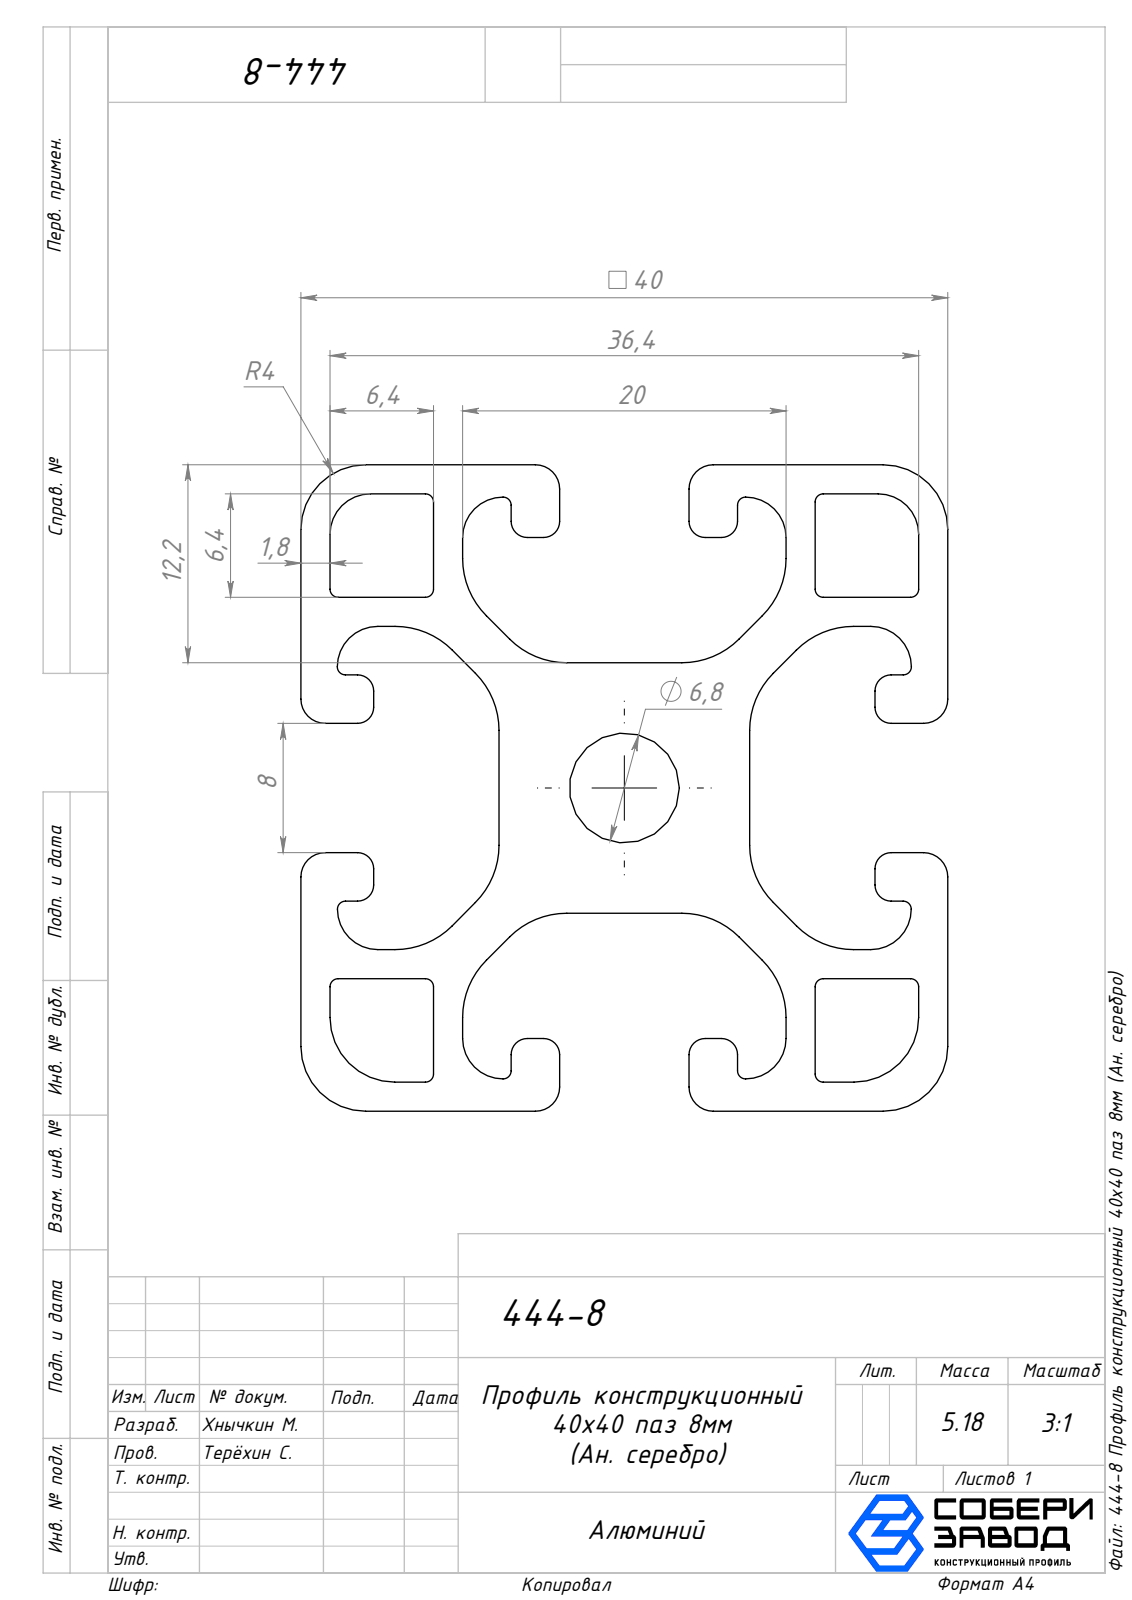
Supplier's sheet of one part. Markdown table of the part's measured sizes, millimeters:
| quantity | value |
| --- | --- |
| part name | V053-8945 |
| STEP written by | SolidWorks 2025 (AUTOMOTIVE_DESIGN) |
| units | millimeters |
| bodies | 1 solid, 144 faces (70 planar, 74 cylindrical, 0 other) |
| overall size | 1000 × 40 × 40 |
| volume | 682 423 mm³ |
| surface area | 461 411 mm² |
| round holes (diameter × count) | 6.8 × 1 |
| partial cylindrical surfaces (radius × count) | 0.5 × 20, 1 × 16, 5 × 16, 1.5 × 8, 2.5 × 8, 4 × 4 |
| main face-to-face distances | 40, 8.2, 31.8, 1.8, 30, 23.6, 3, 16, 24, 7.8 |
